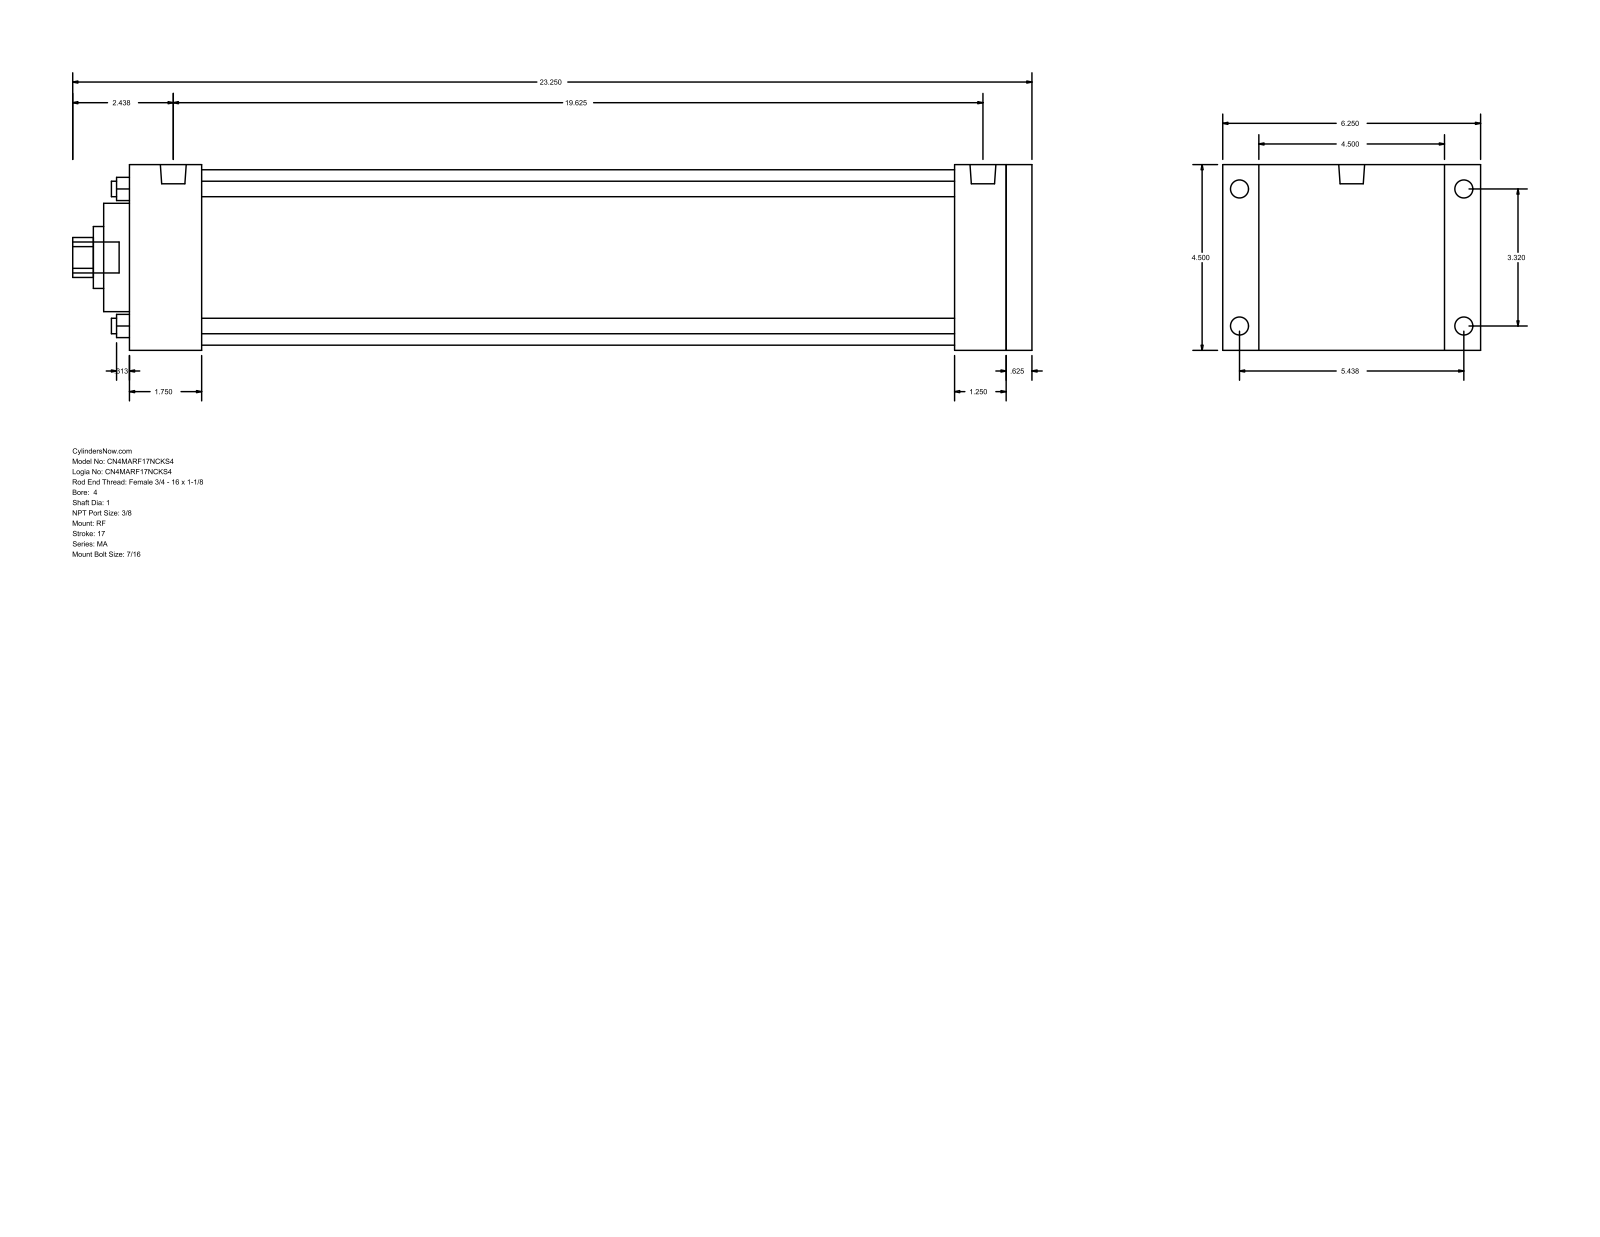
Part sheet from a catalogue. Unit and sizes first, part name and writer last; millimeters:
Units: millimetres
Overall size (bounding box): 590.55 × 158.75 × 114.3
Round holes (diameter × count): ⌀9.53 ×4, ⌀25.4 ×1, ⌀38.1 ×1, ⌀66.67 ×1, ⌀107.95 ×1
Round bosses / shafts (diameter × count): ⌀11.11 ×8, ⌀15.93 ×2, ⌀19.05 ×1
Partial cylindrical surfaces — rounded edges, fillets, slot ends (radius × count): R12.29 ×1
Main face-to-face distances: 114.3, 555.63, 539.75, 15.88, 22.23, 136.53, 508, 31.75, 47.63, 44.46
Hole centre spacings: 59.62, 84.32, 119.25
Bodies: 0 solids, 94 faces (65 planar, 29 cylindrical, 0 other)
Part name (STEP PRODUCT): MA_RF__0400_1
STEP written by: GSSL Pune (CONFIG_CONTROL_DESIGN)
